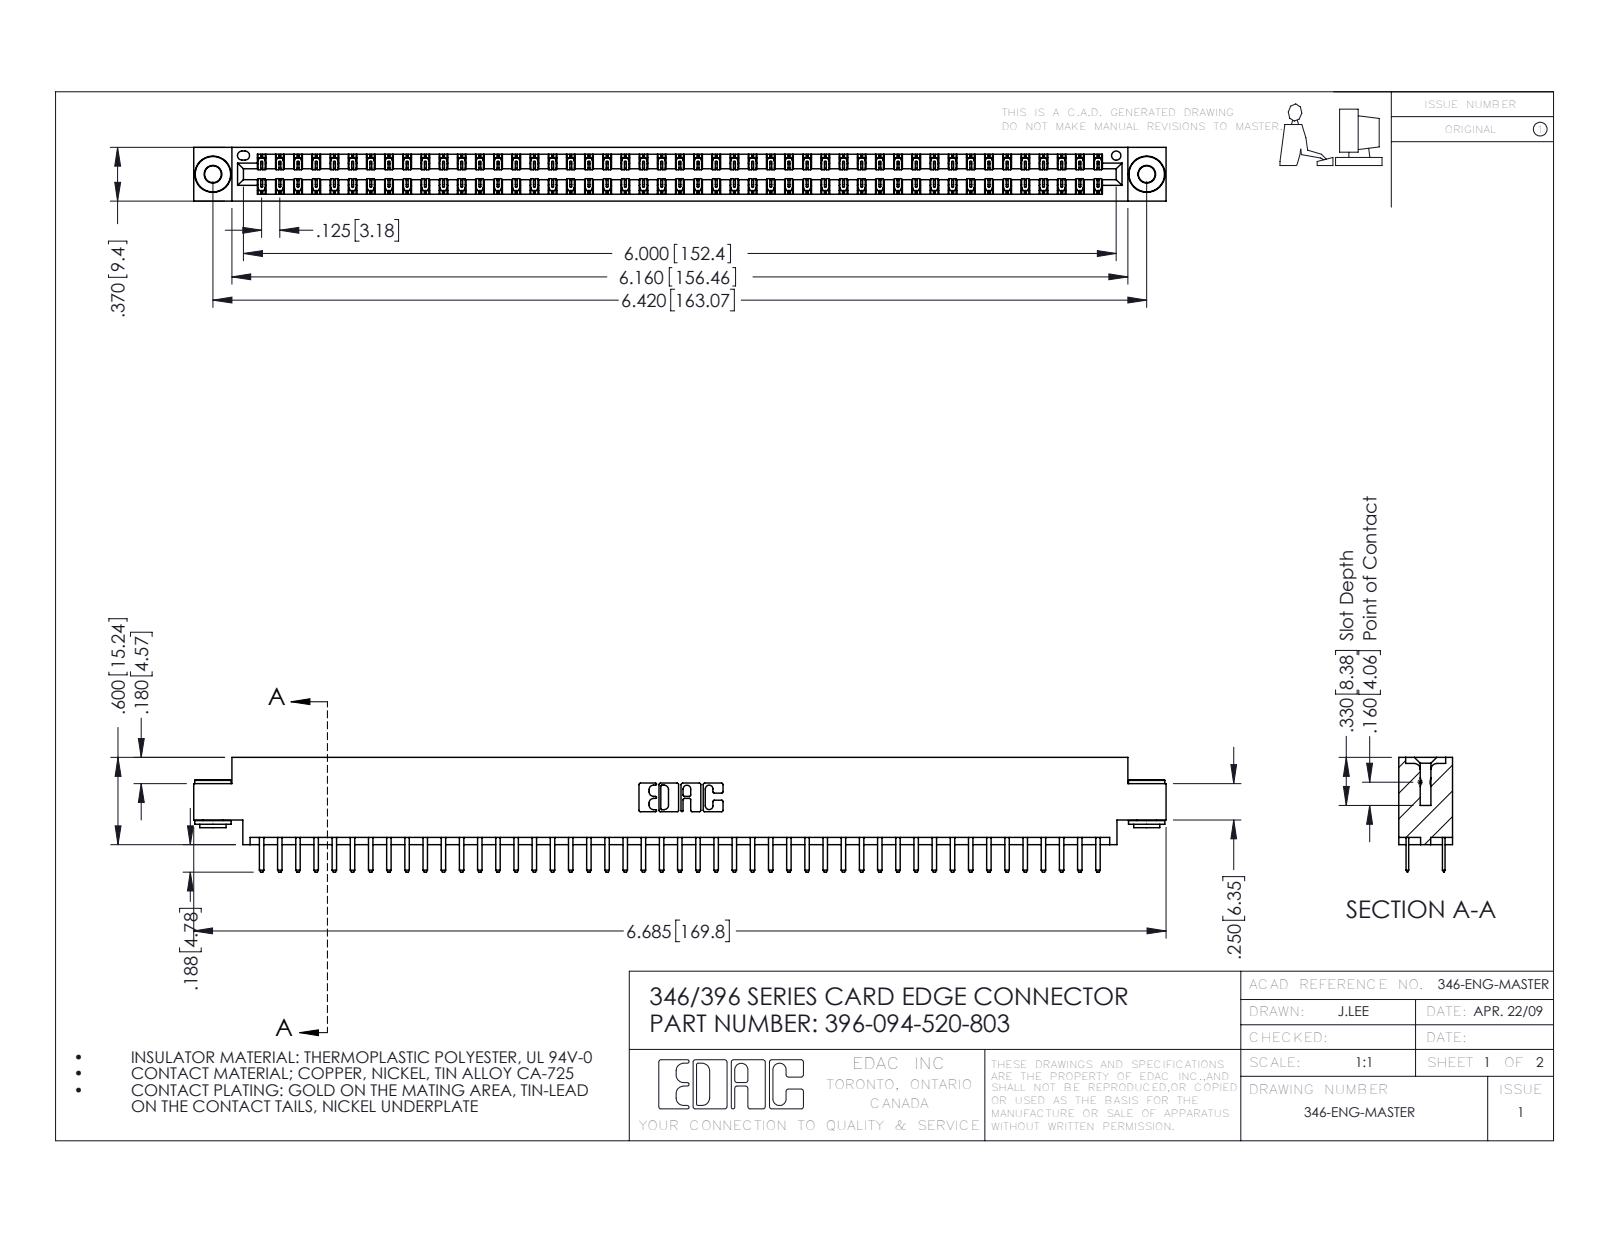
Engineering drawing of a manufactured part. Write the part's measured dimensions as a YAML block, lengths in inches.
part_name: "345-292-001_345-293-120; 345-250-002_345-250-002-102; 396-094-520-803; 346 Part_0.170 Offset - 0.156 Dia-TH"
step_written_by: "SolidWorks 2016 (CONFIG_CONTROL_DESIGN)"
units: inches
bodies: {solids: 97, faces: 5428, planar: 3568, cylindrical: 1852, other: 8}
overall_size: [6.685, 0.788, 0.37]
volume: 1.002
surface_area: 35.57
round_holes:
  - {diameter: 0.116, count: 2}
  - {diameter: 0.156, count: 2}
  - {diameter: 0.064, count: 1}
round_bosses_or_shafts:
  - {diameter: 0.25, count: 2}
  - {diameter: 0.18, count: 2}
  - {diameter: 0.136, count: 2}
partial_cylinders:
  - {radius: 0.006, count: 141}
  - {radius: 0.01, count: 98}
  - {radius: 0.01, count: 22}
  - {radius: 0.007, count: 6}
  - {radius: 0.031, count: 6}
  - {radius: 0.026, count: 3}
  - {radius: 0.014, count: 2}
  - {radius: 0.022, count: 2}
face_to_face_distances: [0.048, 0.322, 0.25, 0.37, 0.025, 0.275, 0.072, 0.298, 0.148, 0.222]
hole_center_spacings: [0.246, 6.211, 6.42]
